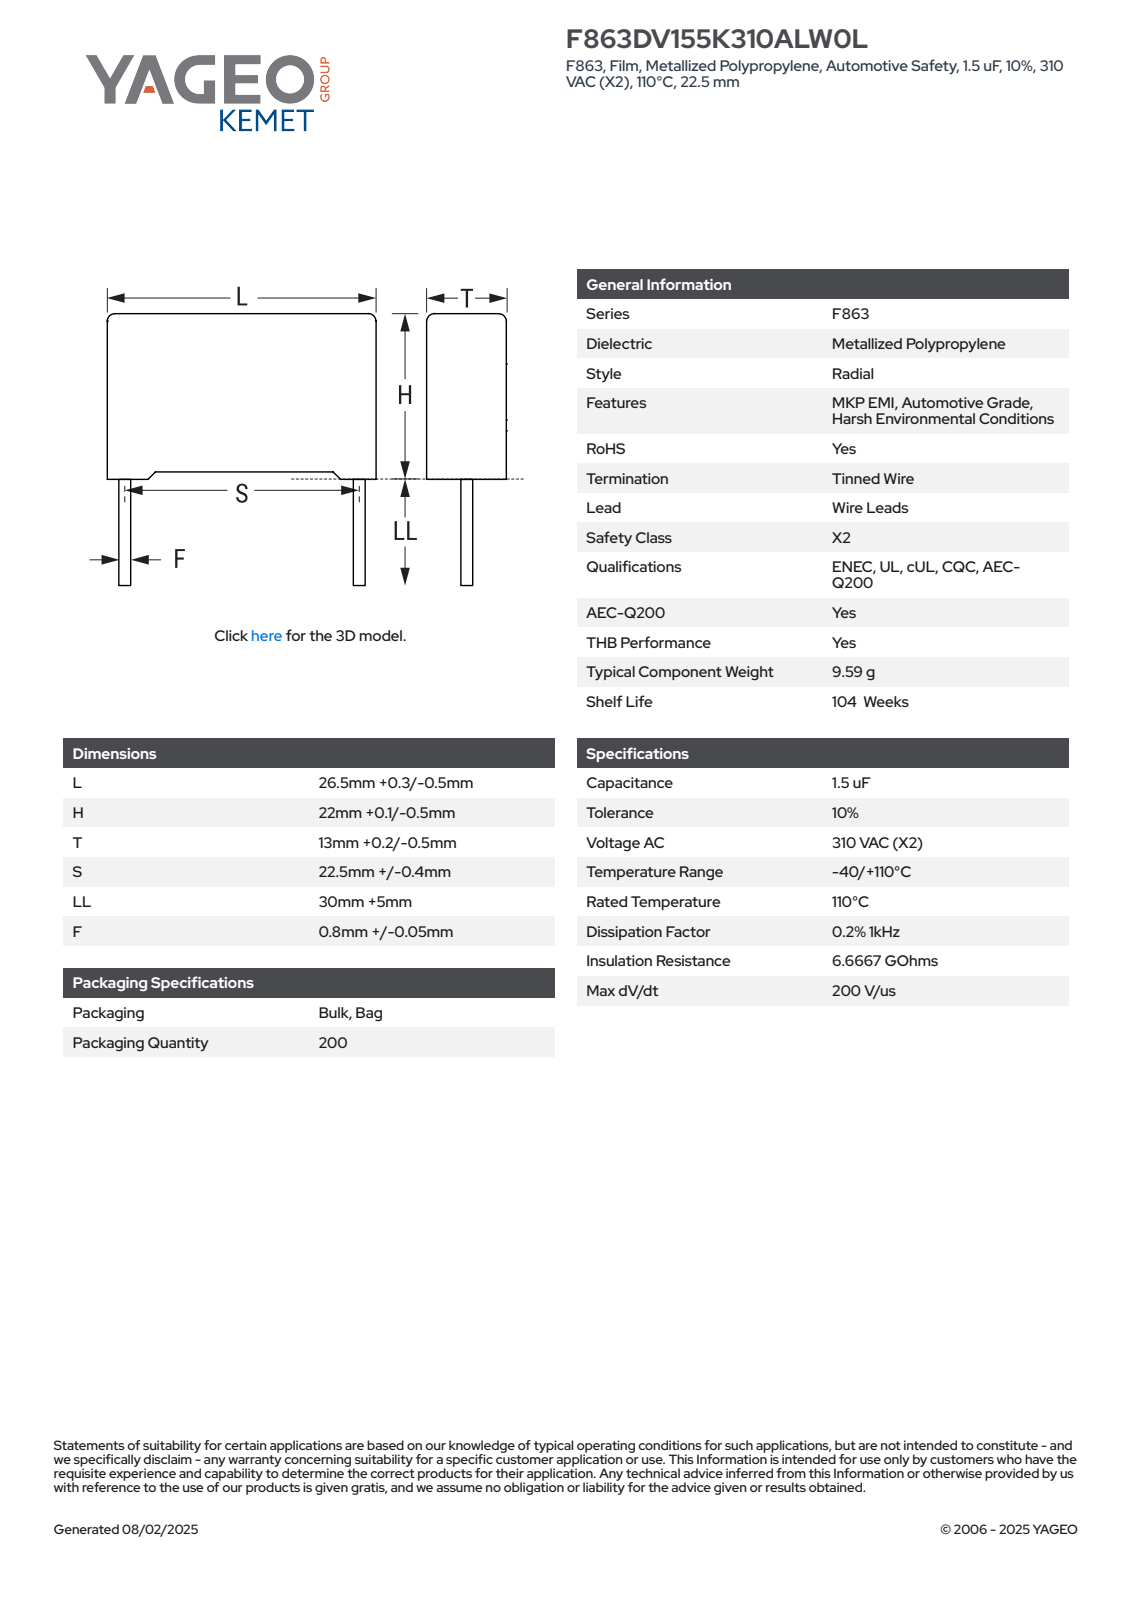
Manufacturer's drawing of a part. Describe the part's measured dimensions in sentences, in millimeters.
The part is named "CFR_RB_26.5X22X13_L26.8H22.1T13.2S22.5LL35F0.85". Its 3-D file was written by "SolidWorks 2014 (AUTOMOTIVE_DESIGN)". It is 4 solids with 89 faces: 81 planar, 8 cylindrical and 0 other. Overall it measures 57.1 by 26.8 by 13.21 millimeters. Its volume is 7 505 cubic millimeters and its surface area 2 644 square millimeters. Round bosses or shafts: 2 of diameter 0.85. Partial cylindrical surfaces (rounded edges, fillets, slot ends): 4 of radius 0.8. The main face-to-face distances are 13.2, 21.11, 26.8, 13.21, 0.6, 12.6, 0.99, 22.1, 0.61, 12.
